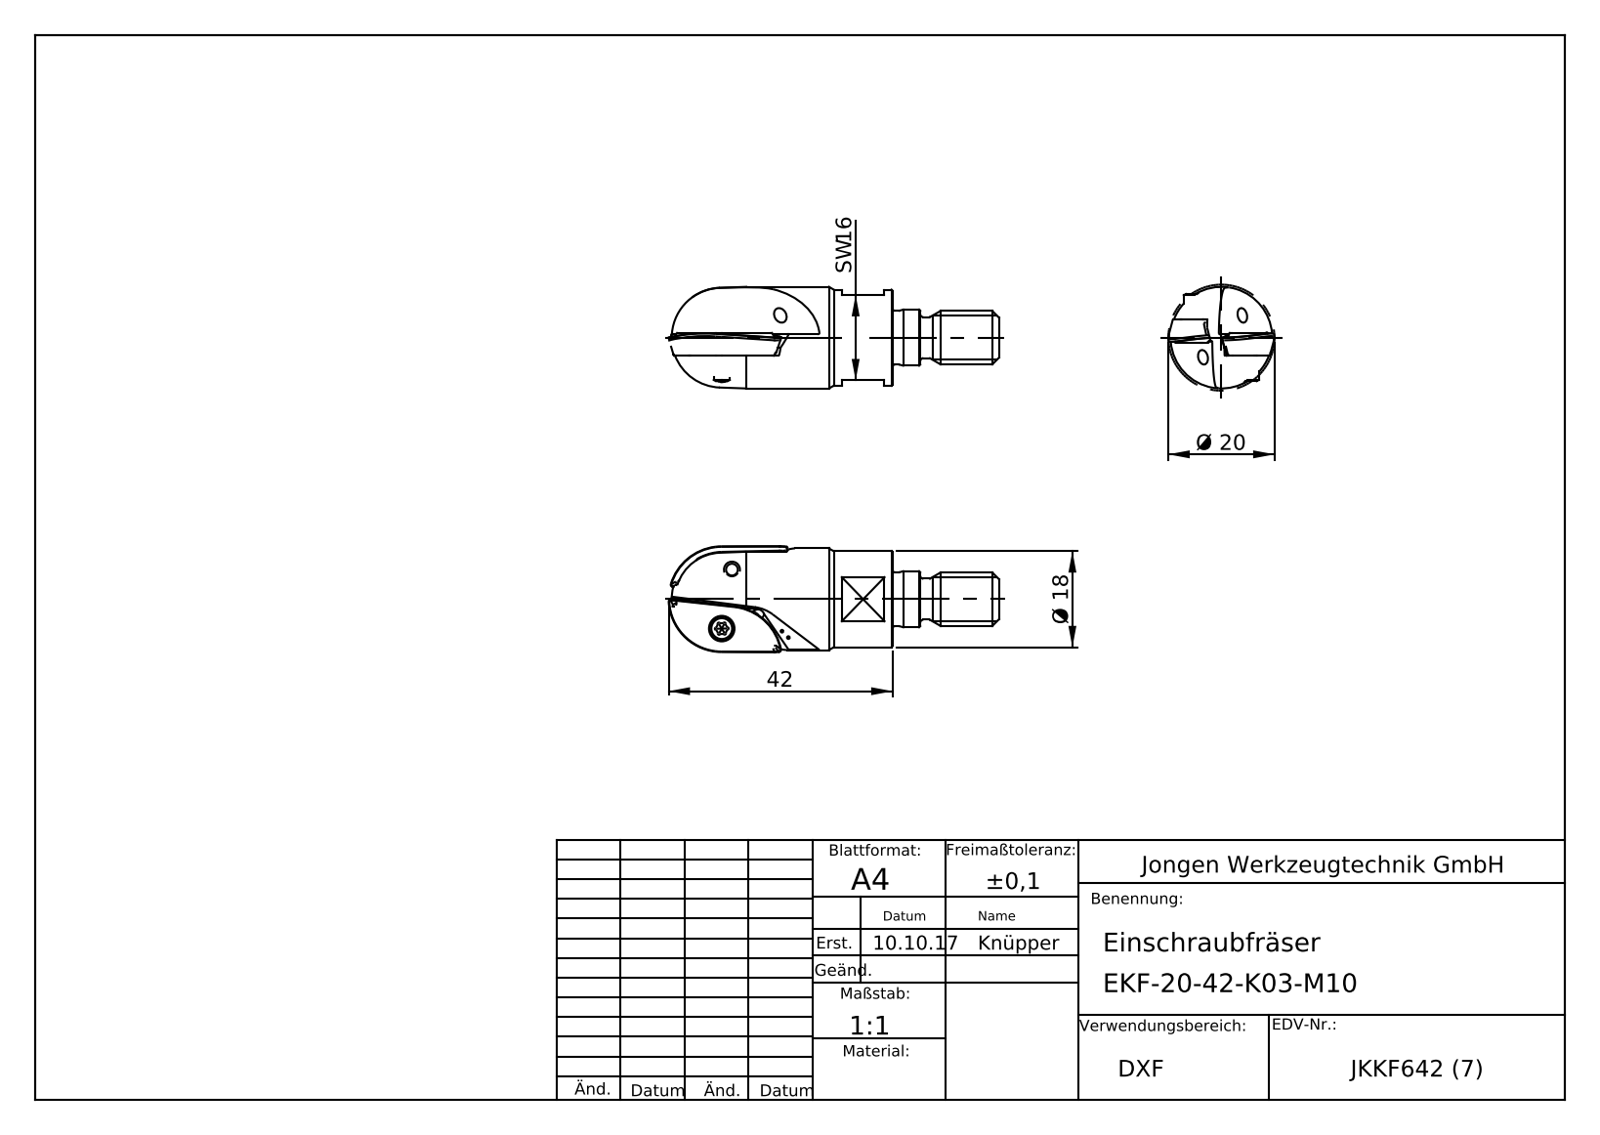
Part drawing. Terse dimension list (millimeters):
name: EKF-20-42-K03-M10
written by: SolidWorks 2019 (AUTOMOTIVE_DESIGN)
unit: mm
bodies: 1 solid, 124 faces (34 planar, 25 cylindrical, 65 other)
size: 62 × 19.9 × 19.9
volume: 11 865 mm³; area: 4 179 mm²
holes: 3× ⌀2.5
bosses: 1× ⌀19.07, 1× ⌀18, 1× ⌀10.5, 1× ⌀10.1, 1× ⌀10, 1× ⌀7.7
rounds: 4× R0.2, 1× R5, 1× R7
face distances: 16, 20, 7.38, 8.62, 8.65, 1.27, 7.35, 5.2, 14.8, 1.5
